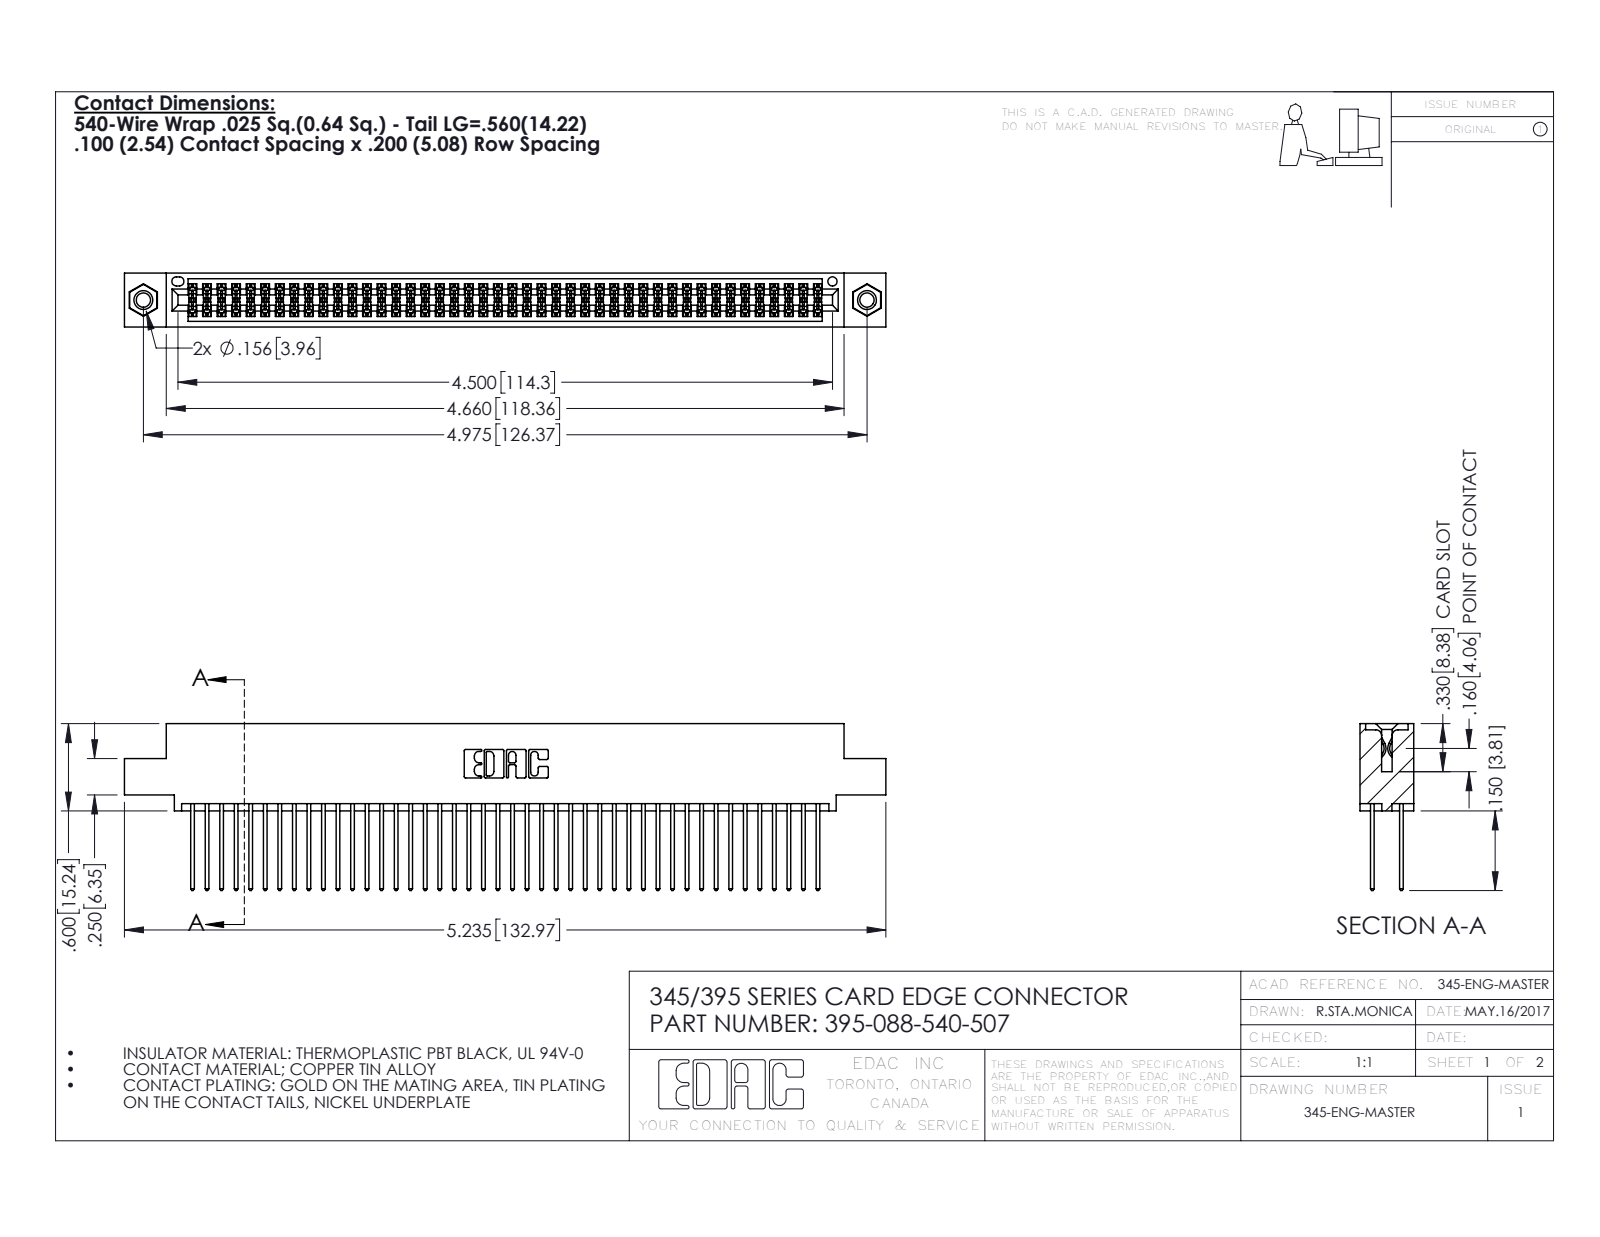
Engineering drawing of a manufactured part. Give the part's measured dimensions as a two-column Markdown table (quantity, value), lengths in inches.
| quantity | value |
| --- | --- |
| part name | 345-292-001_345-293-140; 345-250-001_345-250-005-103; 345 Part_0.110 Offset - 0.156 Dia-TI; 395-088-540-507 |
| STEP written by | SolidWorks 2016 (CONFIG_CONTROL_DESIGN) |
| units | inches |
| bodies | 91 solids, 4590 faces (3020 planar, 1554 cylindrical, 16 other) |
| overall size | 5.235 × 1.147 × 0.37 |
| volume | 0.804 in³ |
| surface area | 32.85 in² |
| round holes (diameter × count) | 0.098 × 2, 0.125 × 2, 0.156 × 2, 0.064 × 1 |
| round bosses / shafts (diameter × count) | 0.155 × 2 |
| partial cylindrical surfaces (radius × count) | 0.006 × 132, 0.01 × 88, 0.01 × 22, 0.007 × 6, 0.031 × 6, 0.026 × 3, 0.014 × 2, 0.019 × 2 |
| main face-to-face distances | 0.072, 0.298, 0.2, 0.098, 0.272, 0.025, 0.37, 0.225, 0.175, 0.149 |
| hole center spacings | 0.27, 4.739, 4.975 |
